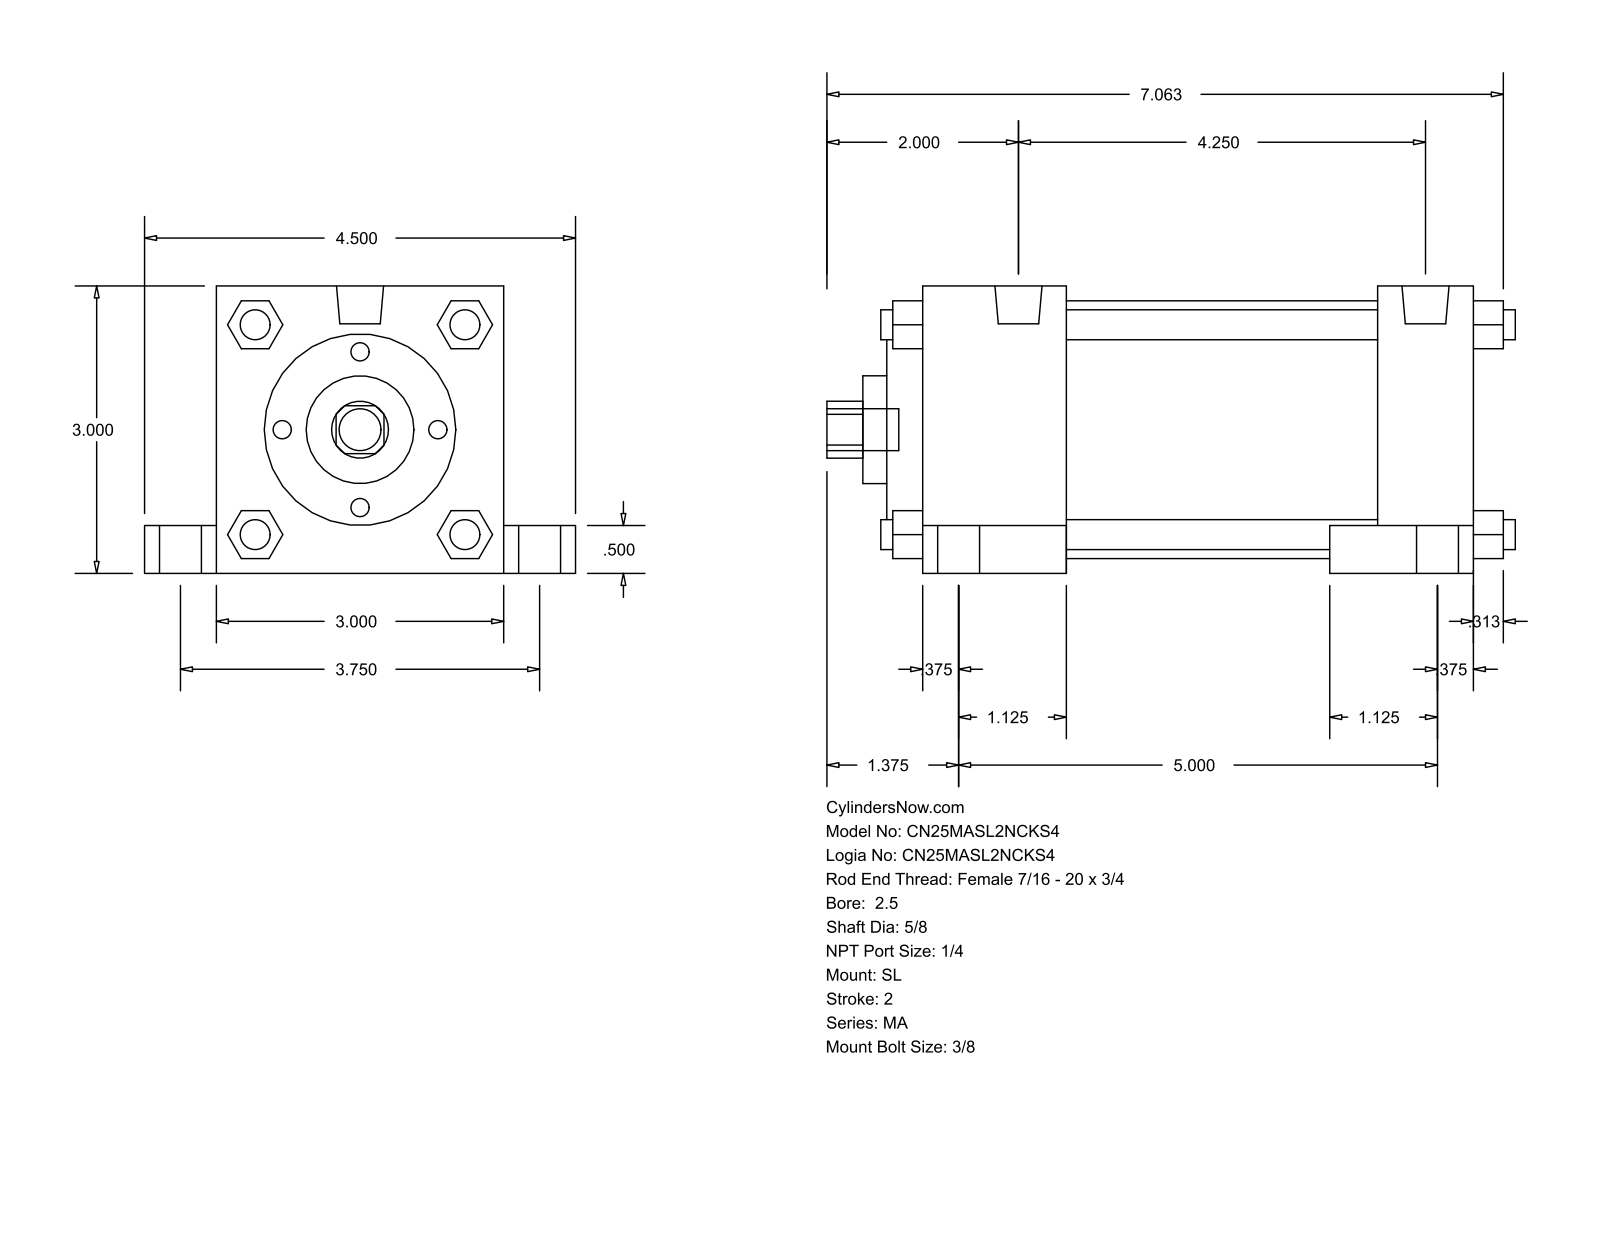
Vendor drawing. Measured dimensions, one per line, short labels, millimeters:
name: MA_SL__0250_0.625
written by: GSSL Pune (CONFIG_CONTROL_DESIGN)
unit: mm
bodies: 0 solids, 150 faces (113 planar, 37 cylindrical, 0 other)
size: 182.56 × 114.3 × 76.2
holes: 1× ⌀15.88, 1× ⌀28.57, 1× ⌀50.8, 1× ⌀68.33
bosses: 8× ⌀7.94, 5× ⌀11.11, 4× ⌀17.46, 2× ⌀12.49
rounds: 1× R7.54
face distances: 76.2, 146.05, 12.7, 82.55, 25.4, 38.1, 107.95, 120.65, 19.05, 63.5
